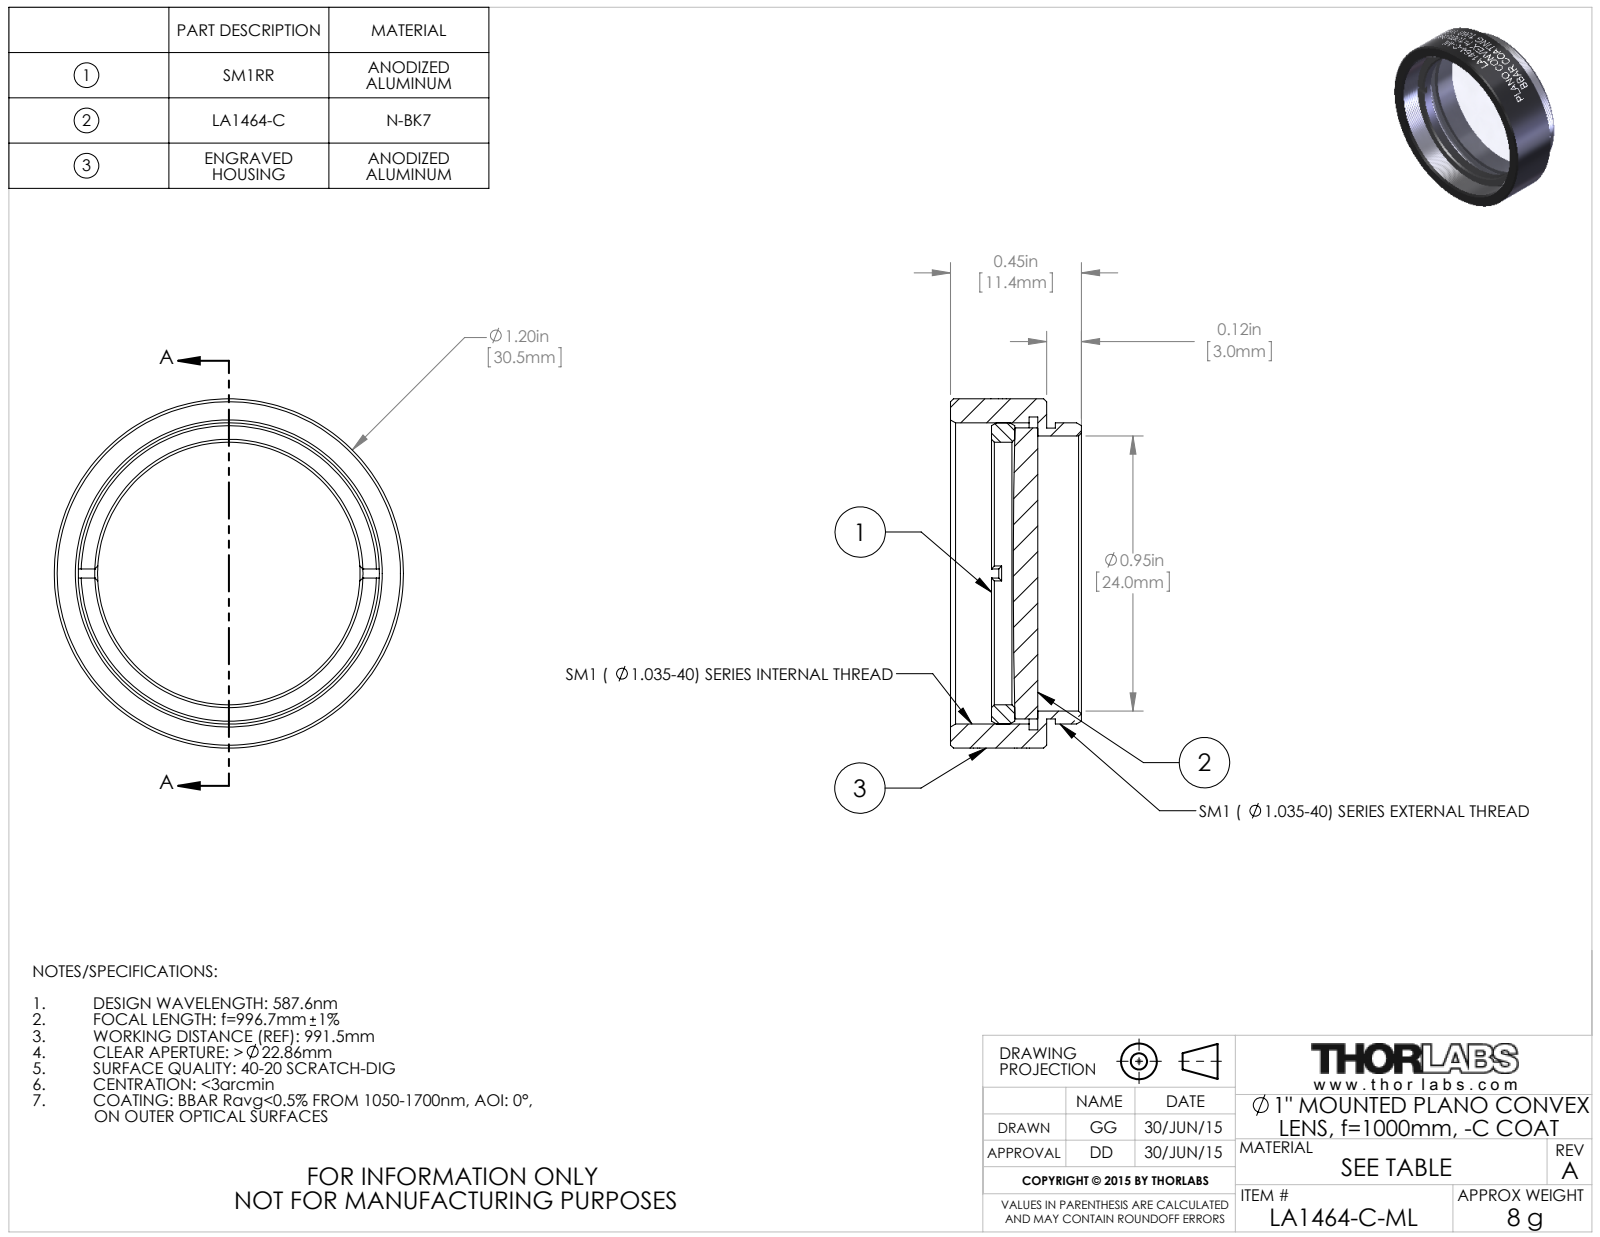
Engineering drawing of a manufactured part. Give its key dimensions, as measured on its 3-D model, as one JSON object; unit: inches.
{"part_name": "TTN039603-E0W", "step_written_by": "SolidWorks 2014 (CONFIG_CONTROL_DESIGN)", "units": "inches", "bodies": {"solids": 3, "faces": 162, "planar": 20, "cylindrical": 114, "other": 28}, "overall_size": [1.2, 1.2, 0.45], "volume_in3": 0.191, "surface_area_in2": 6.674, "round_holes": [[0.902, 1], [0.945, 1], [1.075, 1]], "round_bosses_or_shafts": [[1.2, 1], [1.035, 1], [1, 1], [0.999, 1]], "face_to_face_distances": [0.03, 0.33, 0.3, 0.109, 0.079, 0.221, 0.189, 0.159, 0.08, 0.141]}
